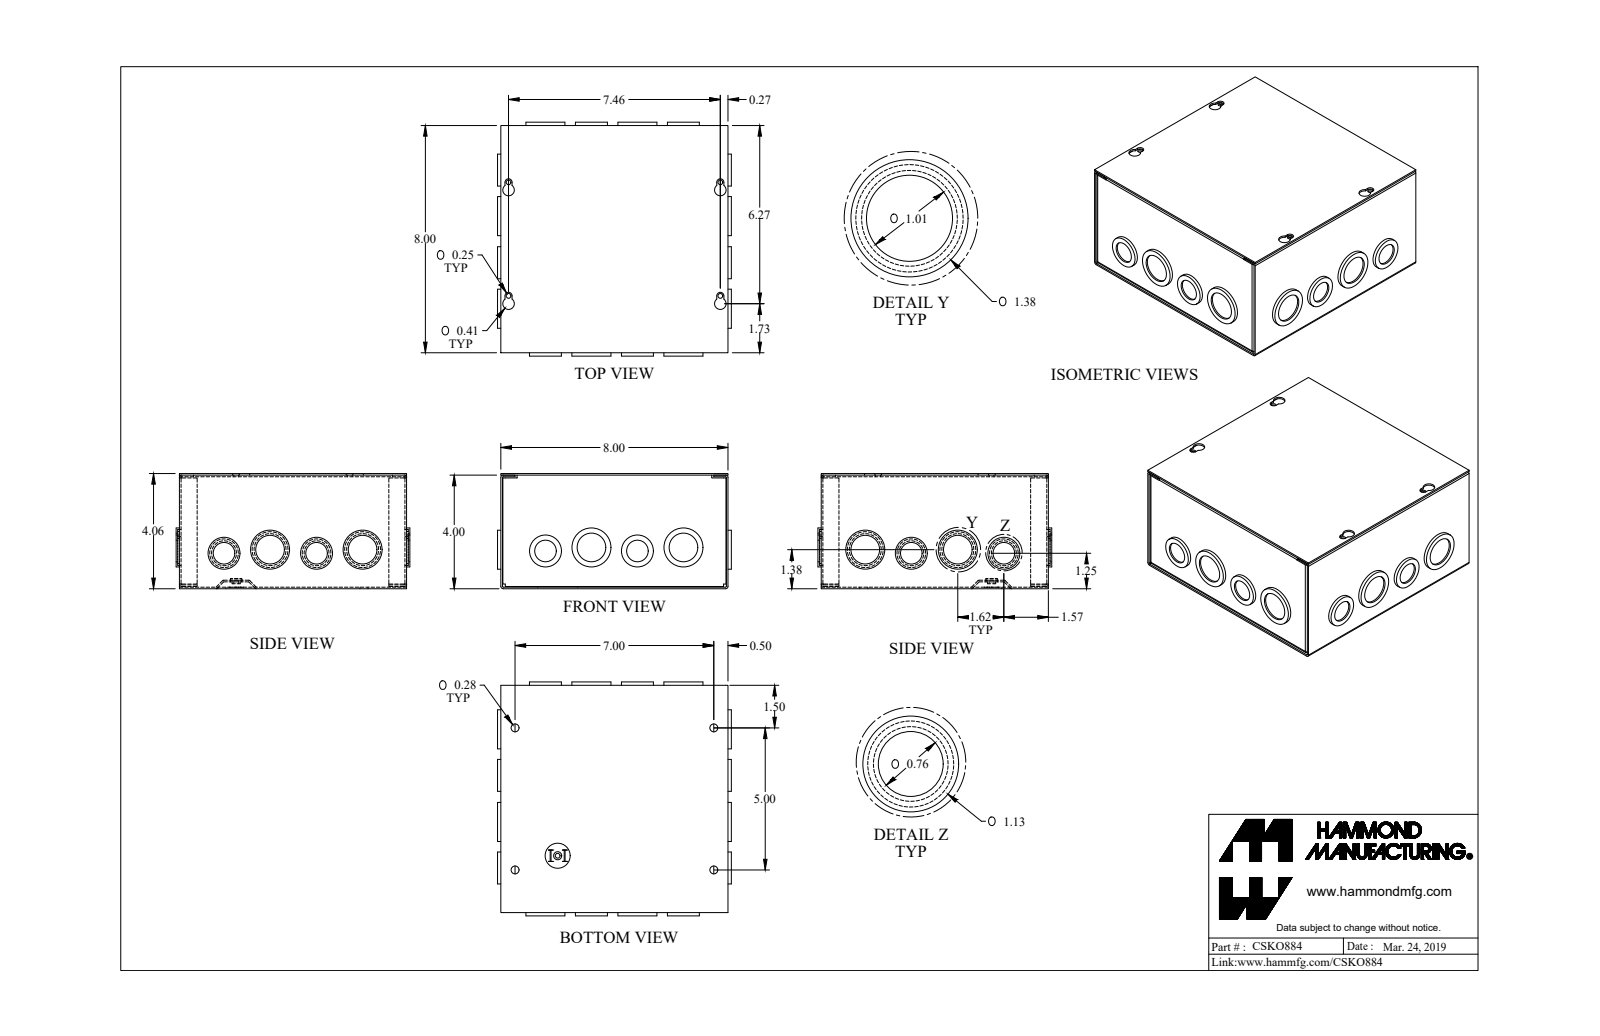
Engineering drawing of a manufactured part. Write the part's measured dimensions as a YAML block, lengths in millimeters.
part_name: "CSKO884_Default"
step_written_by: "SolidWorks 2019 (CONFIG_CONTROL_DESIGN)"
units: millimeters
bodies: {solids: 4, faces: 397, planar: 189, cylindrical: 200, other: 8}
overall_size: [209.1, 209.1, 103]
volume: 271000
surface_area: 380100
round_holes:
  - {diameter: 25.7, count: 12}
  - {diameter: 19.3, count: 6}
  - {diameter: 32, count: 6}
  - {diameter: 4.3, count: 5}
  - {diameter: 7.1, count: 4}
  - {diameter: 12.7, count: 1}
round_bosses_or_shafts:
  - {diameter: 28.6, count: 7}
  - {diameter: 22.2, count: 6}
  - {diameter: 34.9, count: 5}
  - {diameter: 28.6, count: 5}
  - {diameter: 22.2, count: 2}
  - {diameter: 34.9, count: 1}
  - {diameter: 12.5, count: 1}
  - {diameter: 7.2, count: 1}
partial_cylinders:
  - {radius: 0.7, count: 12}
  - {radius: 2.2, count: 12}
  - {radius: 1.4, count: 8}
  - {radius: 3.2, count: 4}
  - {radius: 5.2, count: 4}
face_to_face_distances: [1.4, 101.6, 201.8, 100.2, 203.2, 103, 200.3, 2.9, 2, 98.1]
hole_center_spacings: [41.3, 3.2, 14, 41.1, 82.3, 82.3, 114.5, 184.1]
